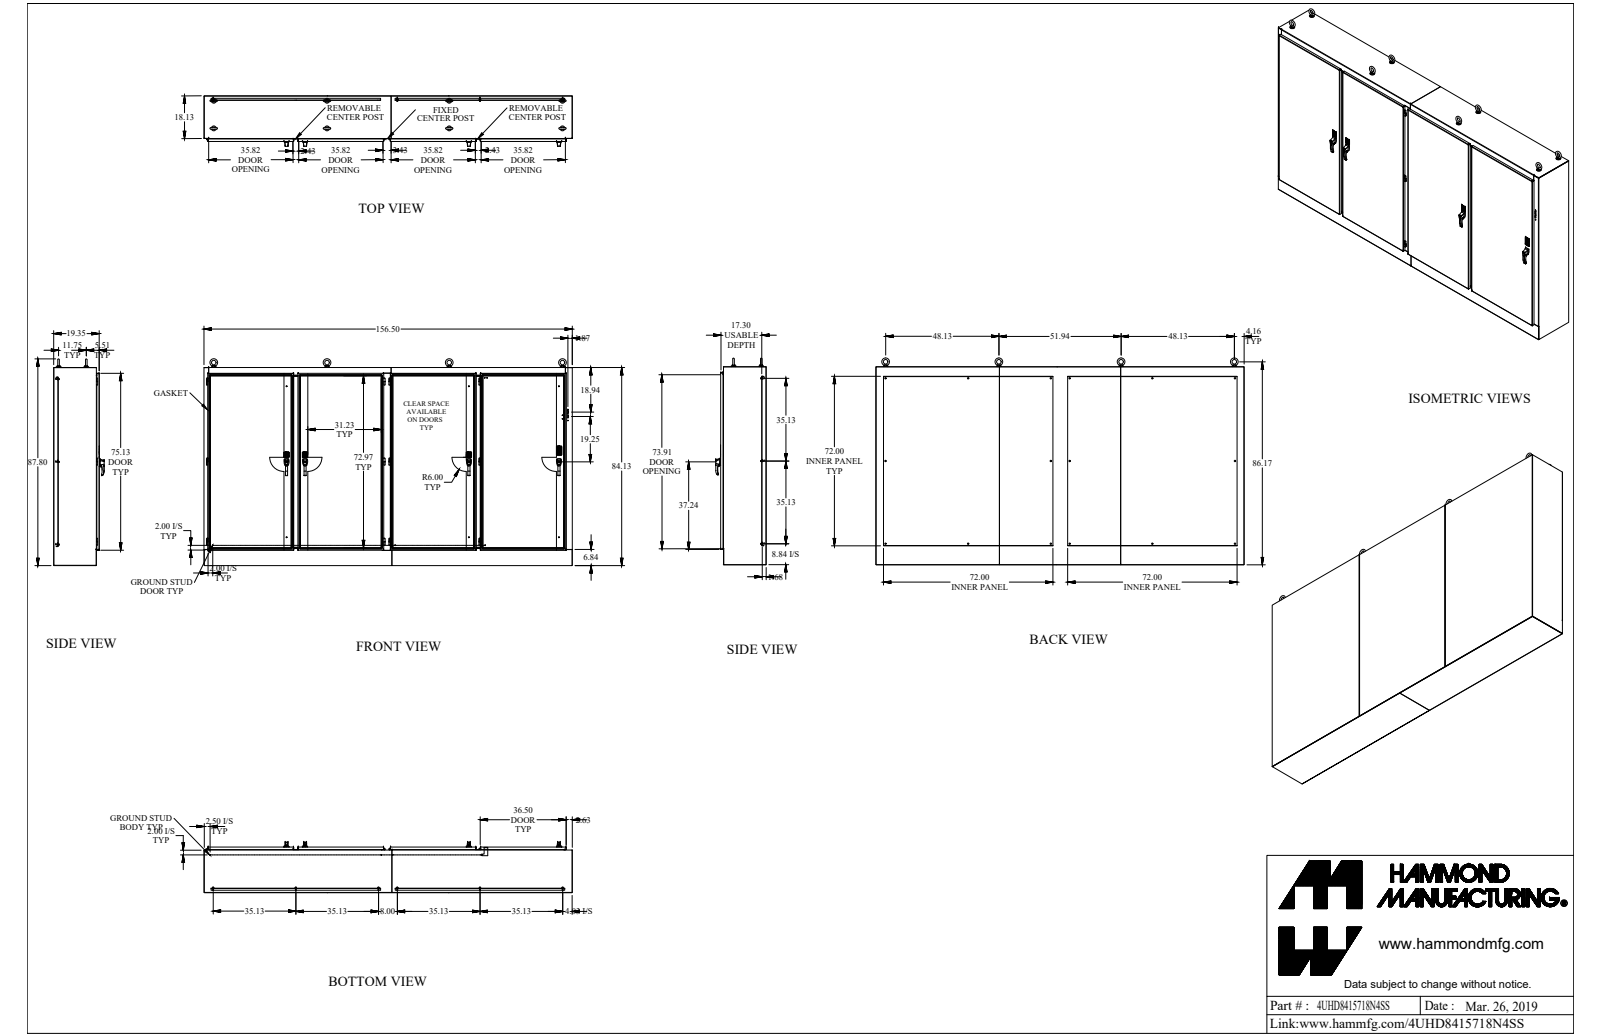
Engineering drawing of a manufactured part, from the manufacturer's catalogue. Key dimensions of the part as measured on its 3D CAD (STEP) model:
Part name (STEP PRODUCT): 4UHD8415718N4SS_1
STEP written by: SolidWorks 2018 (AUTOMOTIVE_DESIGN)
Units: inches
Bodies: 365 solids, 5216 faces (3243 planar, 1478 cylindrical, 495 other)
Overall size (bounding box): 156.5 × 87.799 × 21.465
Volume: 5 873 in³ · Surface area: 111 483 in²
Round holes (diameter × count): ⌀0.25 ×35, ⌀0.196 ×23, ⌀0.307 ×16, ⌀0.281 ×14, ⌀0.266 ×11, ⌀0.445 ×11, ⌀0.201 ×9, ⌀0.313 ×9, ⌀0.39 ×8, ⌀0.642 ×8, ⌀0.813 ×8, ⌀0.257 ×7
Round bosses / shafts (diameter × count): ⌀1 ×26, ⌀0.246 ×19, ⌀0.375 ×17, ⌀0.65 ×16, ⌀0.332 ×16, ⌀0.486 ×13, ⌀0.25 ×11, ⌀0.625 ×10
Partial cylindrical surfaces — rounded edges, fillets, slot ends (radius × count): R0.125 ×88, R0.06 ×71, R0.048 ×46, R0.143 ×46, R0.25 ×45, R0.5 ×44, R0.185 ×31, R0.03 ×24
Main face-to-face distances: 0.095, 0.12, 17.461, 19.274, 19.369, 19.154, 19.248, 17.341, 1.812, 1.907
Hole centre spacings: 77.5, 1.72, 70.25, 1.287, 2.251, 4.268, 7.87, 7.938
